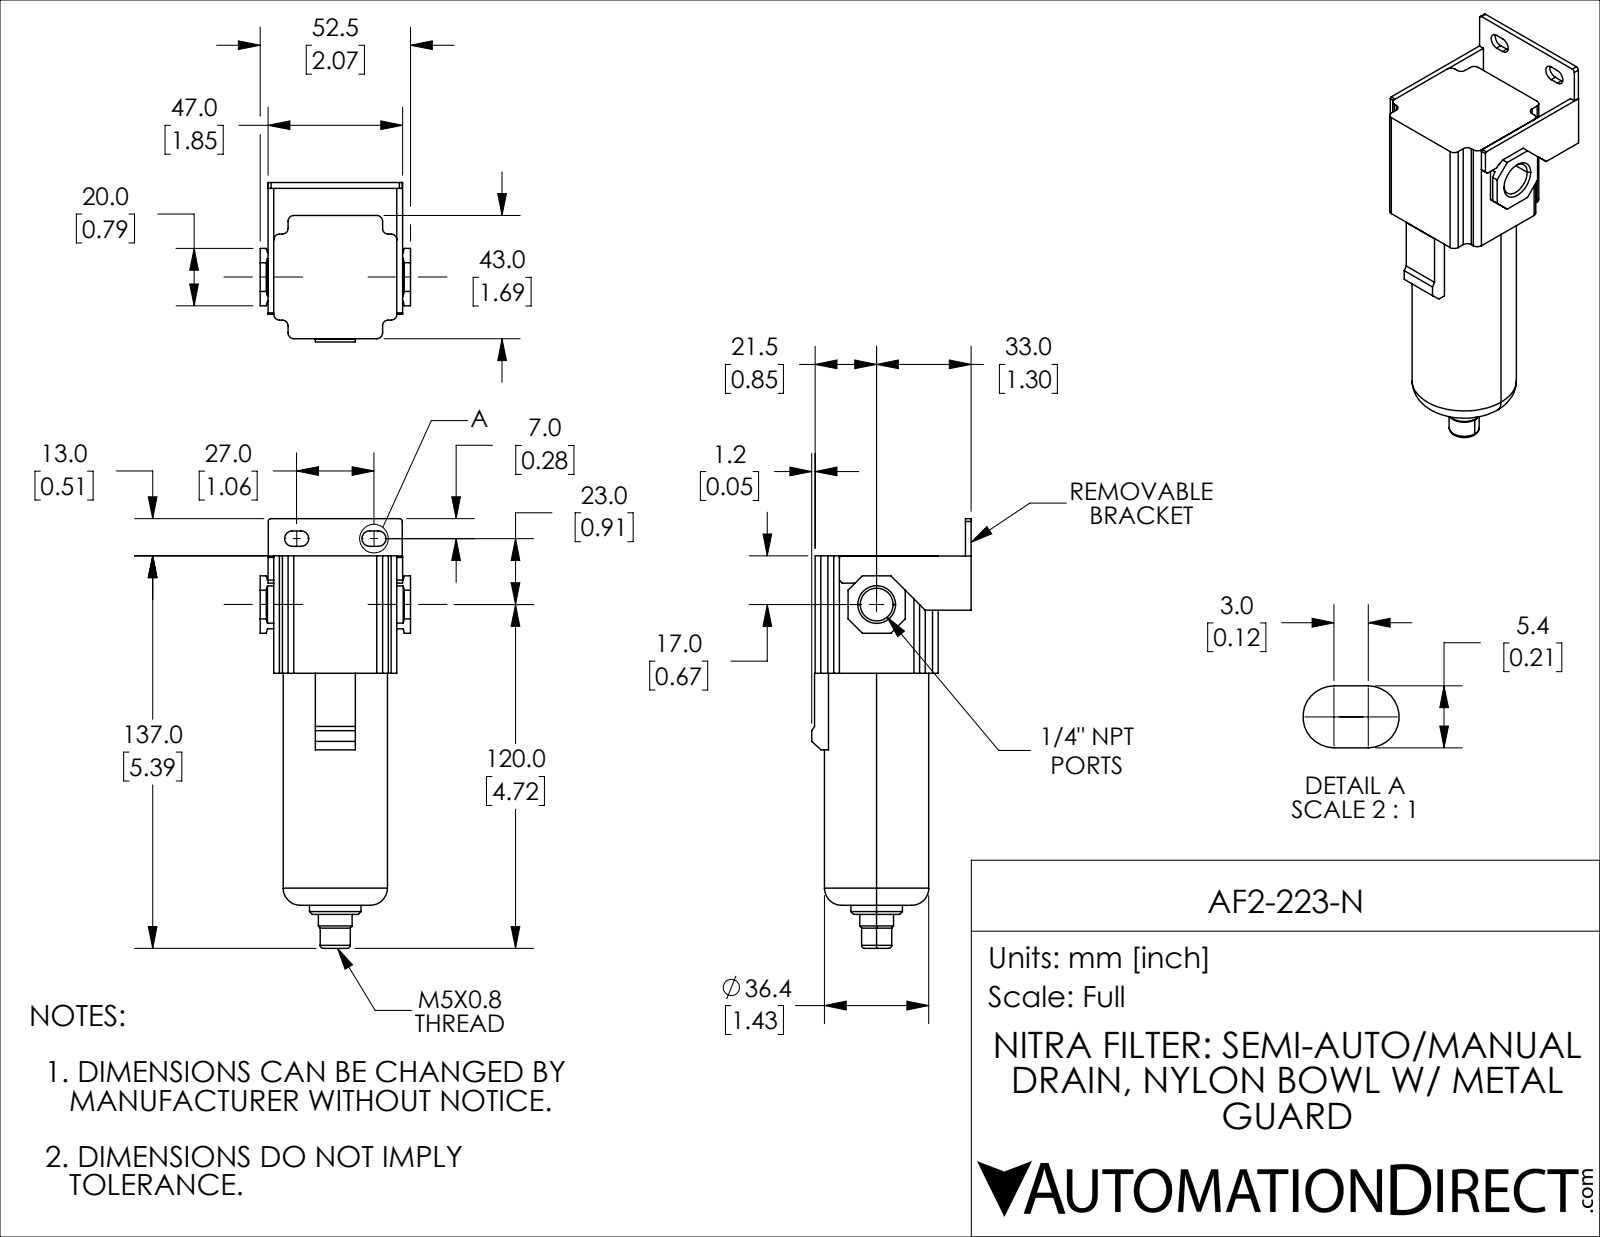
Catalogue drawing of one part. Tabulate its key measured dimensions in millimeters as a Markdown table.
| quantity | value |
| --- | --- |
| part name | AF2-223-N |
| STEP written by | SolidWorks 2019 (CONFIG_CONTROL_DESIGN) |
| units | millimeters |
| bodies | 1 solid, 136 faces (90 planar, 32 cylindrical, 14 other) |
| overall size | 150 × 55.67 × 52.5 |
| volume | 162 539 mm³ |
| surface area | 26 433 mm² |
| round holes (diameter × count) | 4.13 × 1, 11.45 × 1 |
| round bosses / shafts (diameter × count) | 36.4 × 1, 18 × 1, 11.8 × 1, 10.5 × 1 |
| partial cylindrical surfaces (radius × count) | 2 × 12, 2.7 × 4, 1 × 2 |
| main face-to-face distances | 2, 43, 9.5, 52.5, 11.5, 45, 54.5, 41, 47, 5 |
